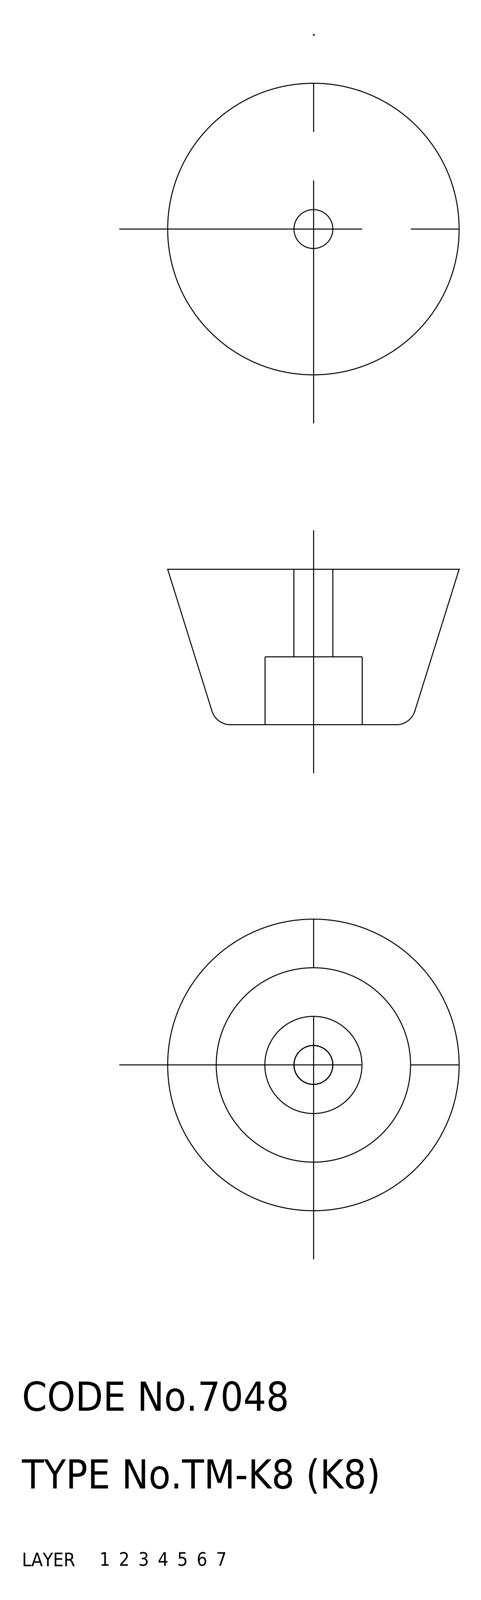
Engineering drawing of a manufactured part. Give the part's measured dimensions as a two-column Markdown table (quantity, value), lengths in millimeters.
| quantity | value |
| --- | --- |
| part name | rubber foot |
| STEP written by | CADfix (AUTOMOTIVE_DESIGN) |
| units | millimeters |
| bodies | 1 solid, 11 faces (0 planar, 0 cylindrical, 11 other) |
| overall size | 30 × 30 × 16 |
| volume | 7 287 mm³ |
| surface area | 2 620 mm² |
